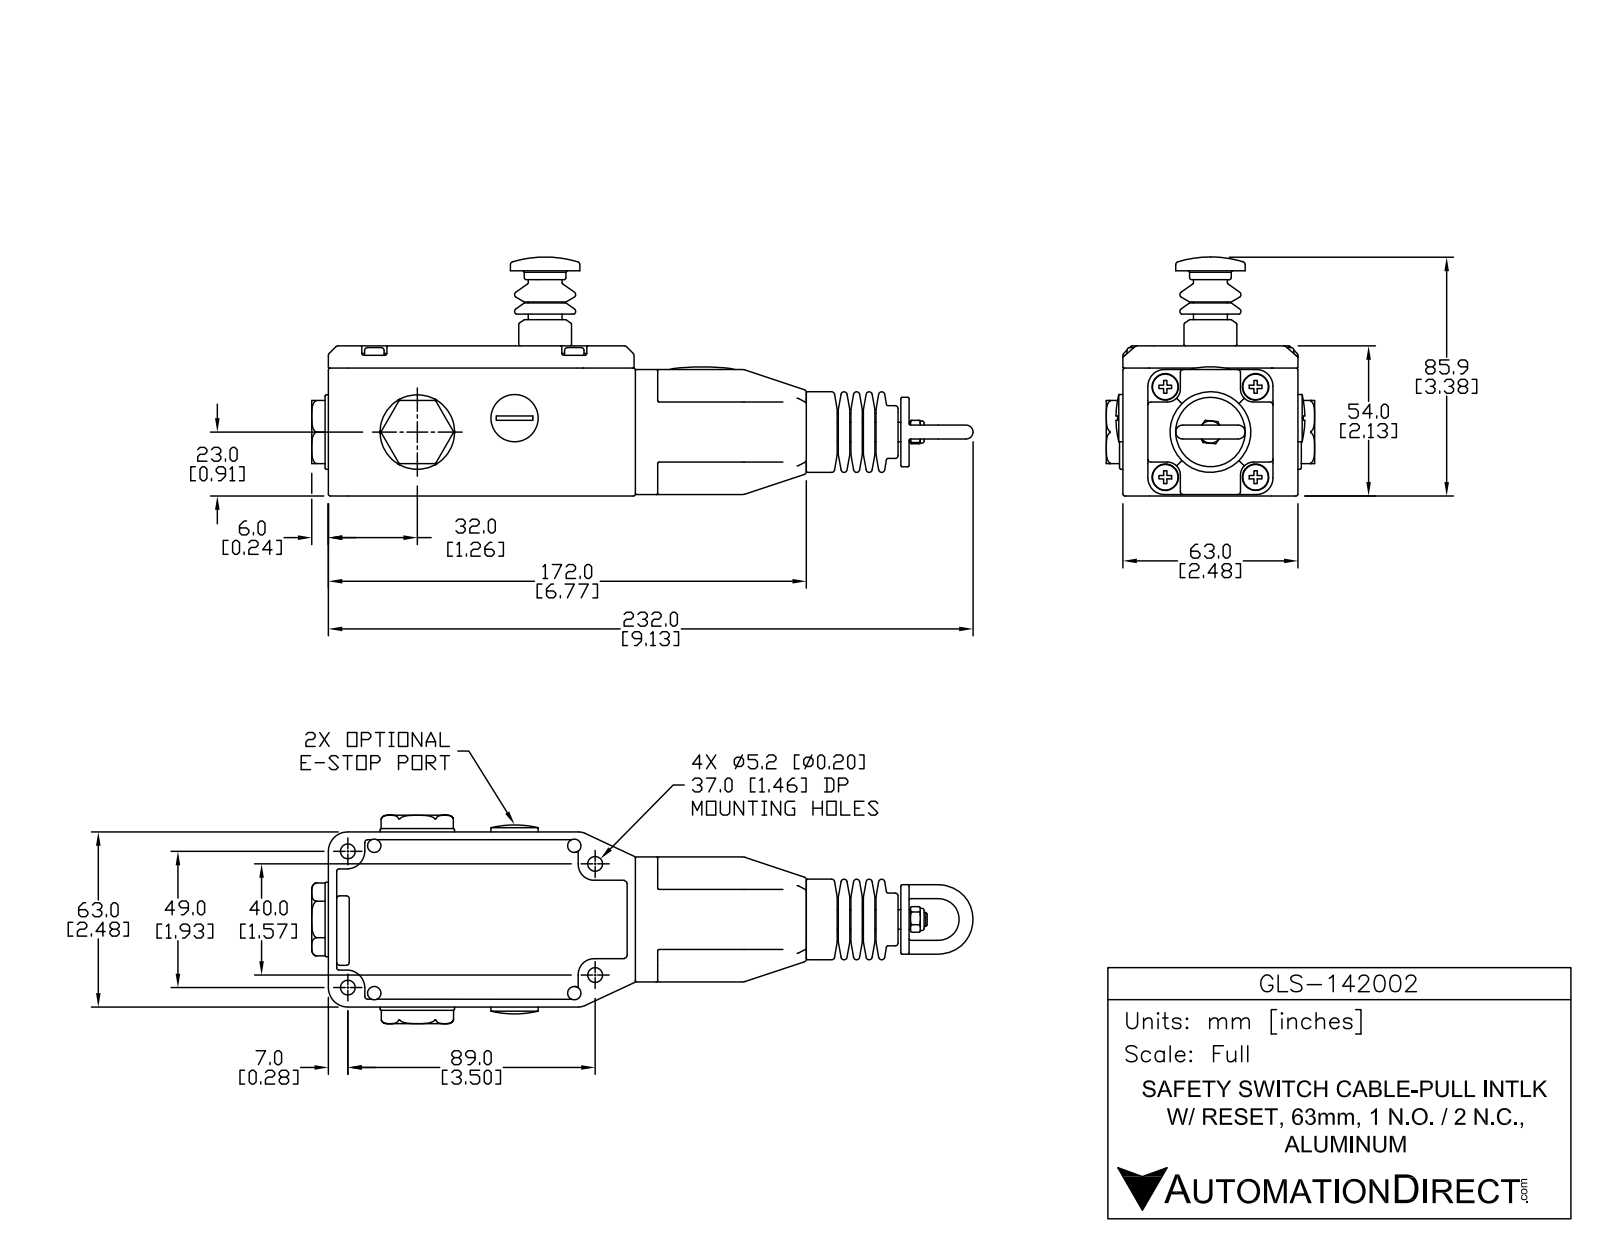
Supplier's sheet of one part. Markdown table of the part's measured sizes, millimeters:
| quantity | value |
| --- | --- |
| part name | GLS-142002 |
| STEP written by | SolidWorks 2013 (AUTOMOTIVE_DESIGN) |
| units | millimeters |
| bodies | 1 solid, 565 faces (188 planar, 183 cylindrical, 194 other) |
| overall size | 239.16 × 86 × 75.6 |
| volume | 482 310 mm³ |
| surface area | 58 090 mm² |
| round holes (diameter × count) | 4.75 × 4, 5 × 4, 9.5 × 4 |
| round bosses / shafts (diameter × count) | 9.2 × 4, 6 × 4, 26.8 × 2, 25 × 2, 19 × 2, 5 × 2, 29 × 1, 17 × 1 |
| partial cylindrical surfaces (radius × count) | 0.5 × 42, 0.75 × 20, 4 × 4, 4.5 × 4, 4.8 × 4, 16 × 4, 7 × 2, 8.2 × 2 |
| main face-to-face distances | 54, 63, 9, 11.7, 33.3, 4.5, 49.5, 45, 27, 16.2 |
| hole center spacings | 9.6, 9.62, 32.4, 32.6, 45.96, 46.61, 51.39, 52 |
